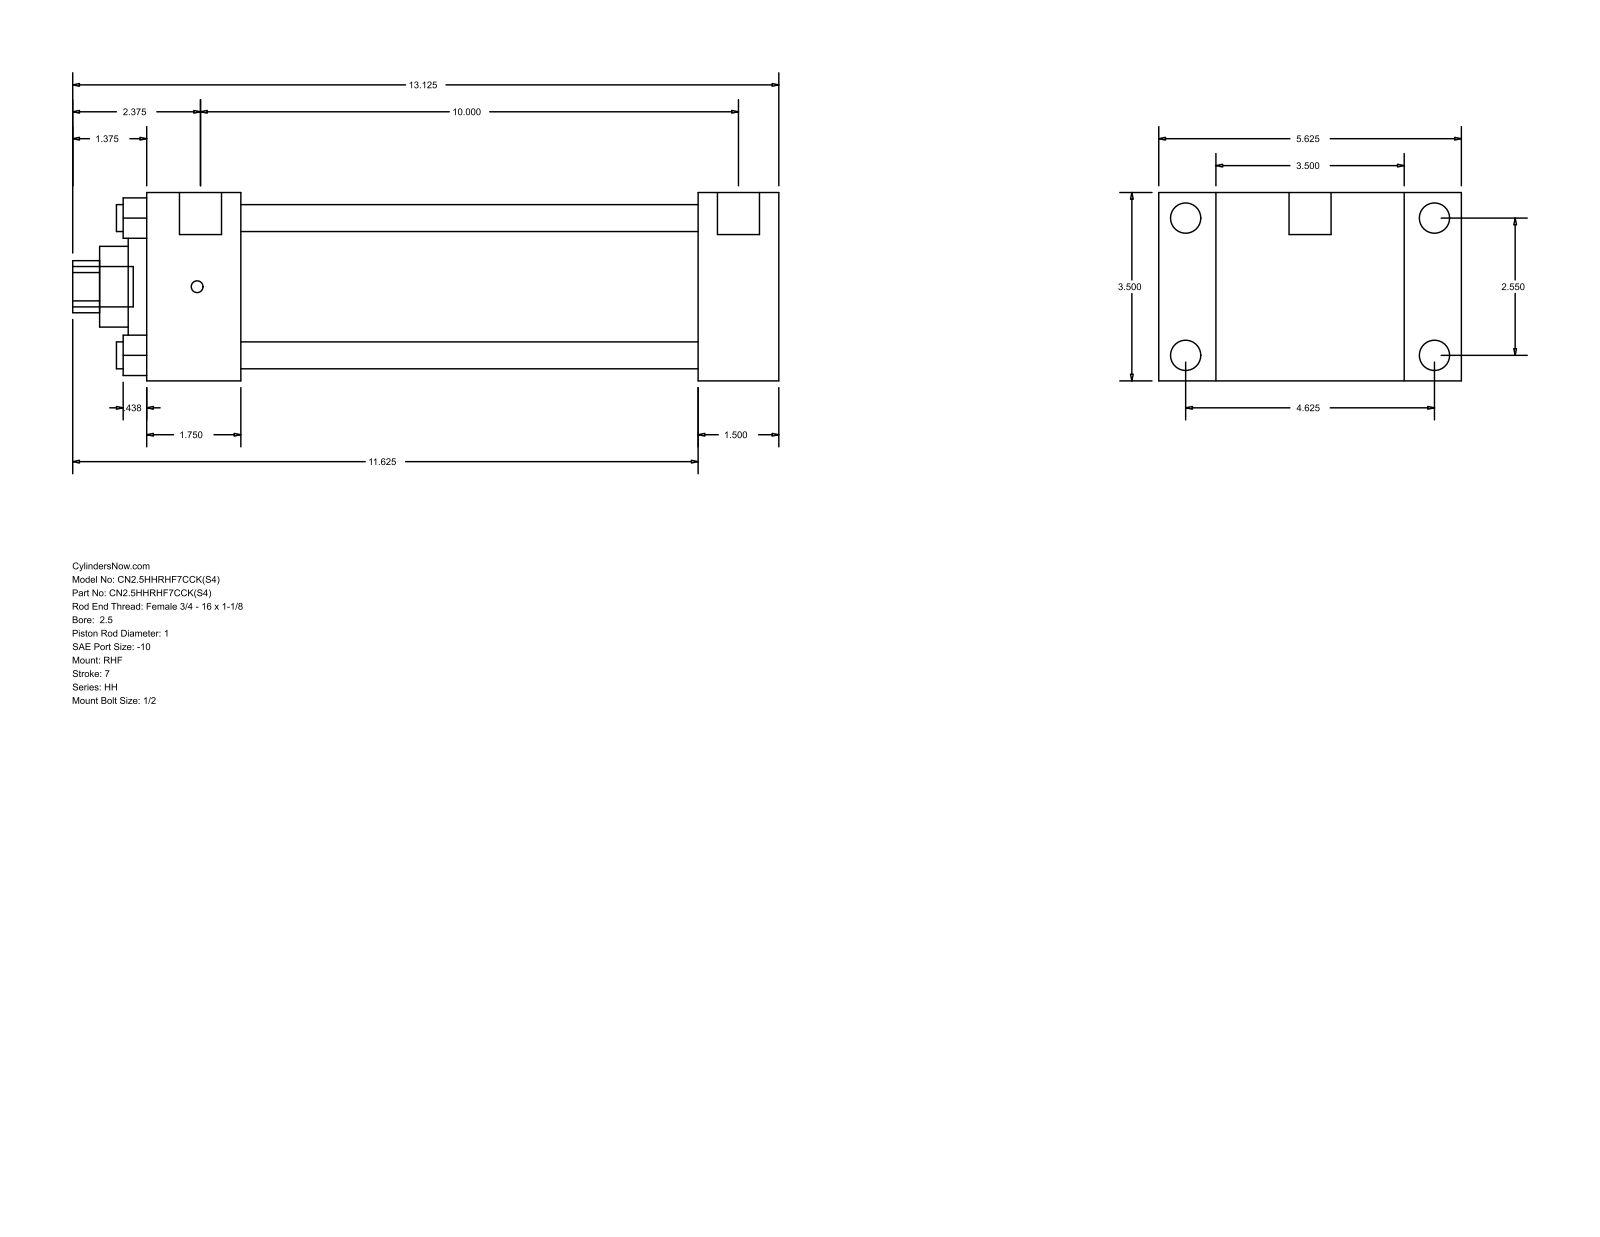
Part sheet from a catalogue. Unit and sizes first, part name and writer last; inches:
Units: inches
Overall size (bounding box): 13.125 × 5.625 × 3.5
Round holes (diameter × count): ⌀0.5 ×4, ⌀1 ×1, ⌀1.5 ×1, ⌀2.375 ×1, ⌀2.875 ×1
Round bosses / shafts (diameter × count): ⌀0.563 ×4, ⌀0.219 ×4, ⌀0.781 ×2, ⌀0.75 ×1
Partial cylindrical surfaces — rounded edges, fillets, slot ends (radius × count): R0.484 ×1
Main face-to-face distances: 3.5, 1.5, 1.063, 4.563, 10.25, 11.75, 5.625, 1.75, 8.5, 10
Hole centre spacings: 1.803, 2.55, 3.606
Bodies: 0 solids, 90 faces (61 planar, 29 cylindrical, 0 other)
Part name (STEP PRODUCT): HH_RHF__0250_1
STEP written by: GSSL Pune (CONFIG_CONTROL_DESIGN)
